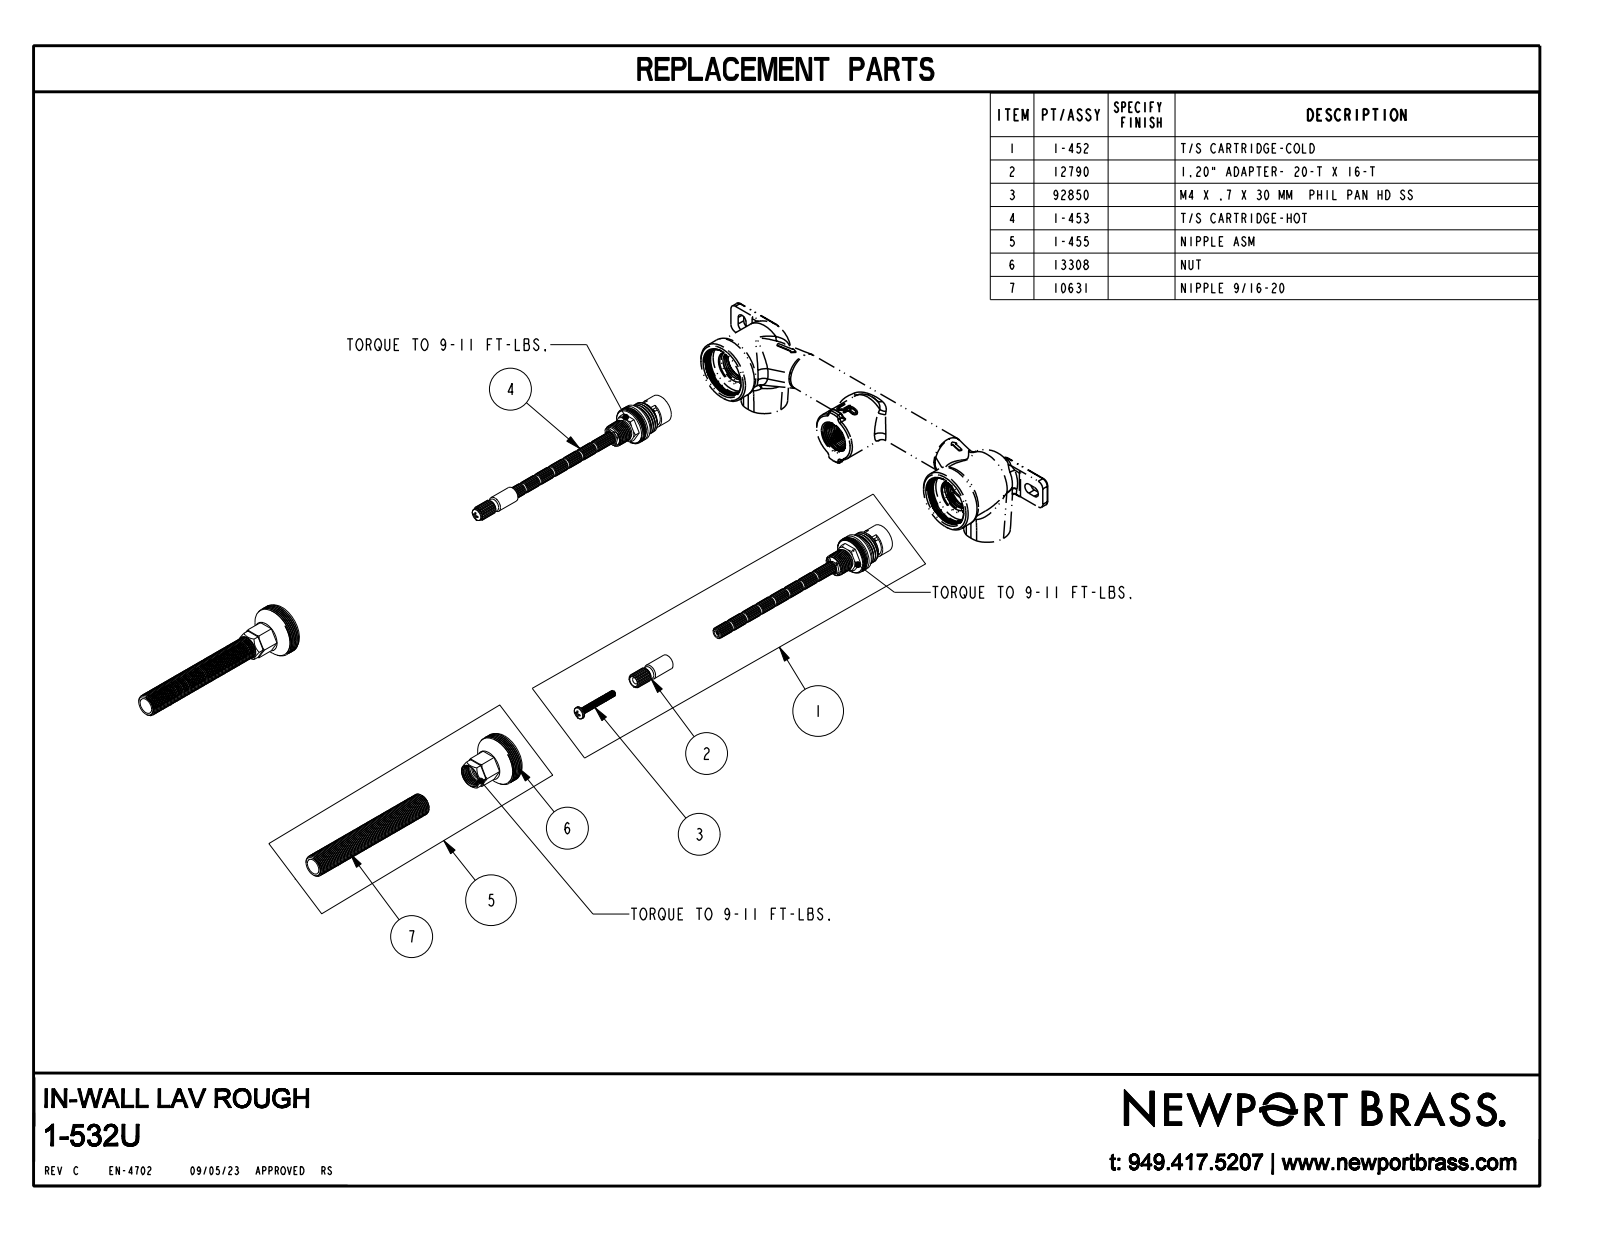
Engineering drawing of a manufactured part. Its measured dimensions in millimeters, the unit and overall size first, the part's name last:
Units: millimetres
Overall size (bounding box): 280 × 238.8 × 60
Round holes (diameter × count): ⌀4.4 ×2, ⌀8.4 ×2, ⌀25.4 ×1
Round bosses / shafts (diameter × count): ⌀40 ×2, ⌀36 ×2, ⌀14.3 ×2, ⌀9.9 ×2, ⌀8.3 ×2, ⌀8 ×2, ⌀4 ×2, ⌀3.1 ×2
Partial cylindrical surfaces — rounded edges, fillets, slot ends (radius × count): R1 ×8, R2 ×8, R2 ×6, R4 ×6, R1 ×2, R1.2 ×2, R1.3 ×2, R3.5 ×2
Main face-to-face distances: 53, 241.4, 5, 48, 40, 40, 40.1, 39.9, 154.6, 149.6
Hole centre spacings: 200
Volume: 421 600 mm³ · Surface area: 68 970 mm²
Bodies: 4 solids, 6205 faces (5459 planar, 488 cylindrical, 258 other)
Part name (STEP PRODUCT): 1-532U_SW0002
STEP written by: CREO PARAMETRIC BY PTC INC, 2018400 (AUTOMOTIVE_DESIGN)
